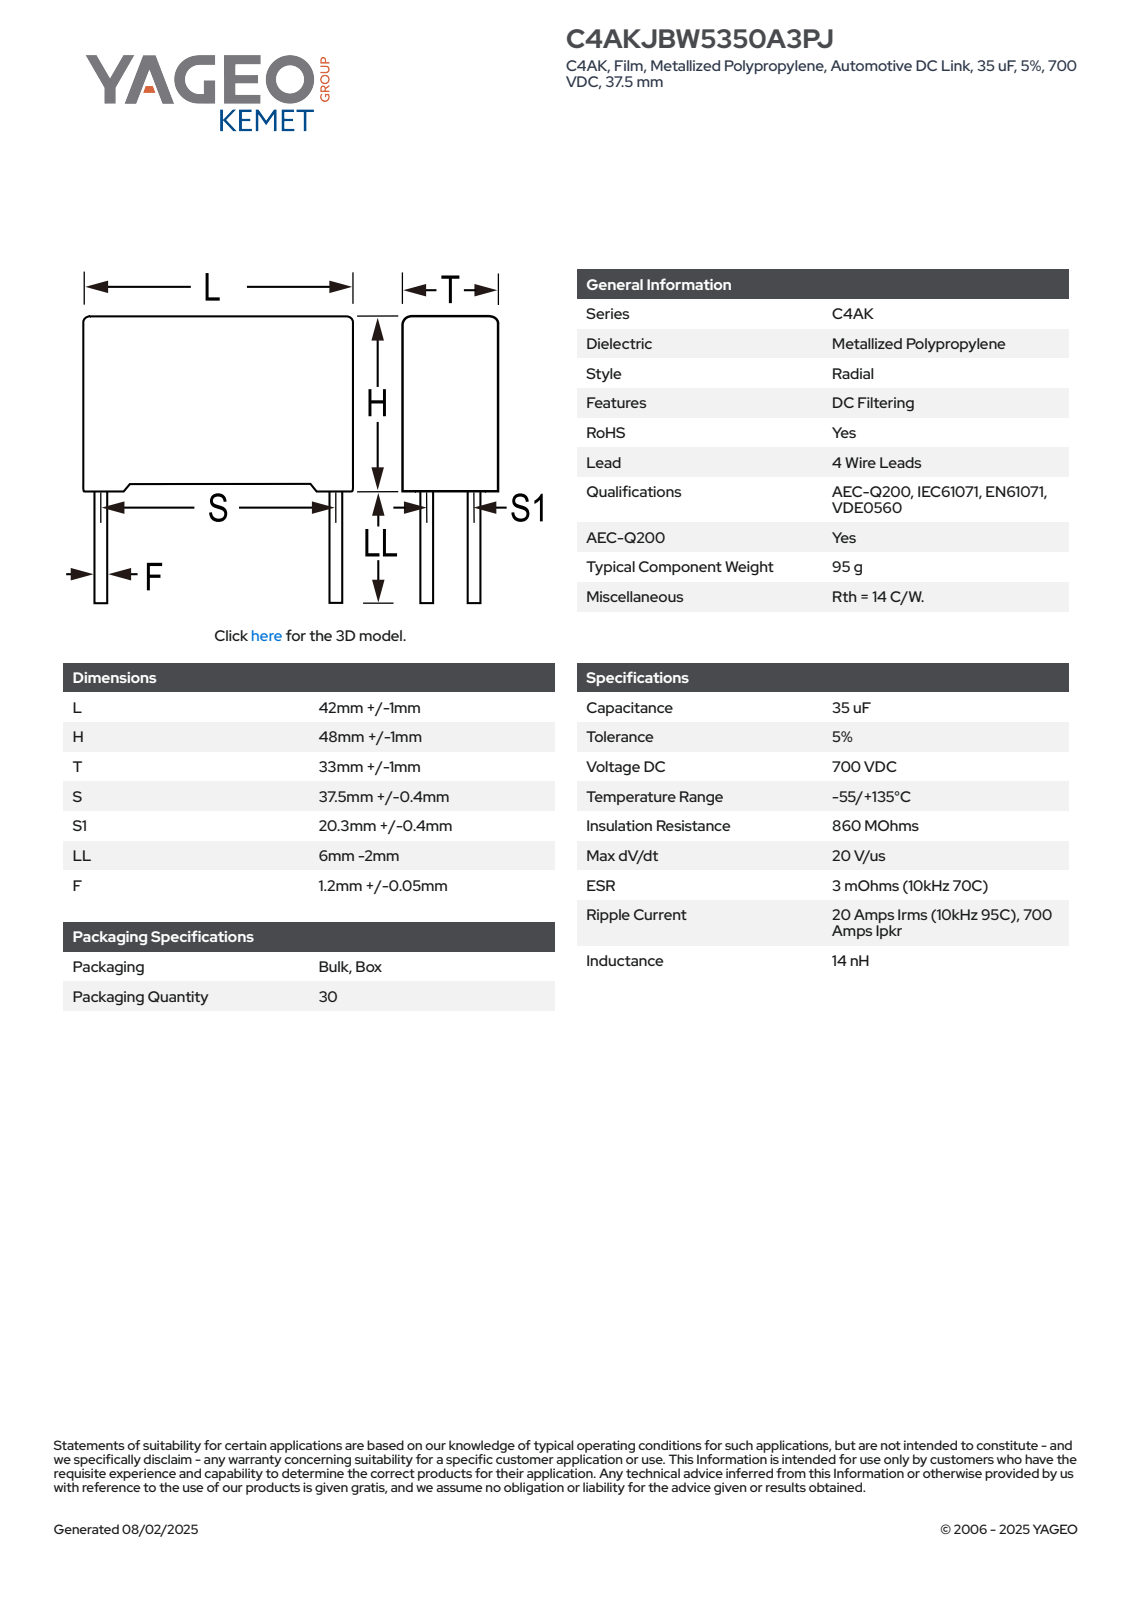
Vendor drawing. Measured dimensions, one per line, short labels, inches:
name: CFP_RB4_42X48X33_L43H49T34S37.5S120.3LL4F1.25
written by: SolidWorks 2014 (AUTOMOTIVE_DESIGN)
unit: in
bodies: 4 solids, 87 faces (79 planar, 8 cylindrical, 0 other)
size: 2.087 × 1.693 × 1.339
volume: 4.261 in³; area: 16.61 in²
bosses: 4× ⌀0.049
face distances: 1.339, 1.693, 1.872, 0.057, 1.929, 0.082, 1.611, 1.339, 1.528, 1.256
